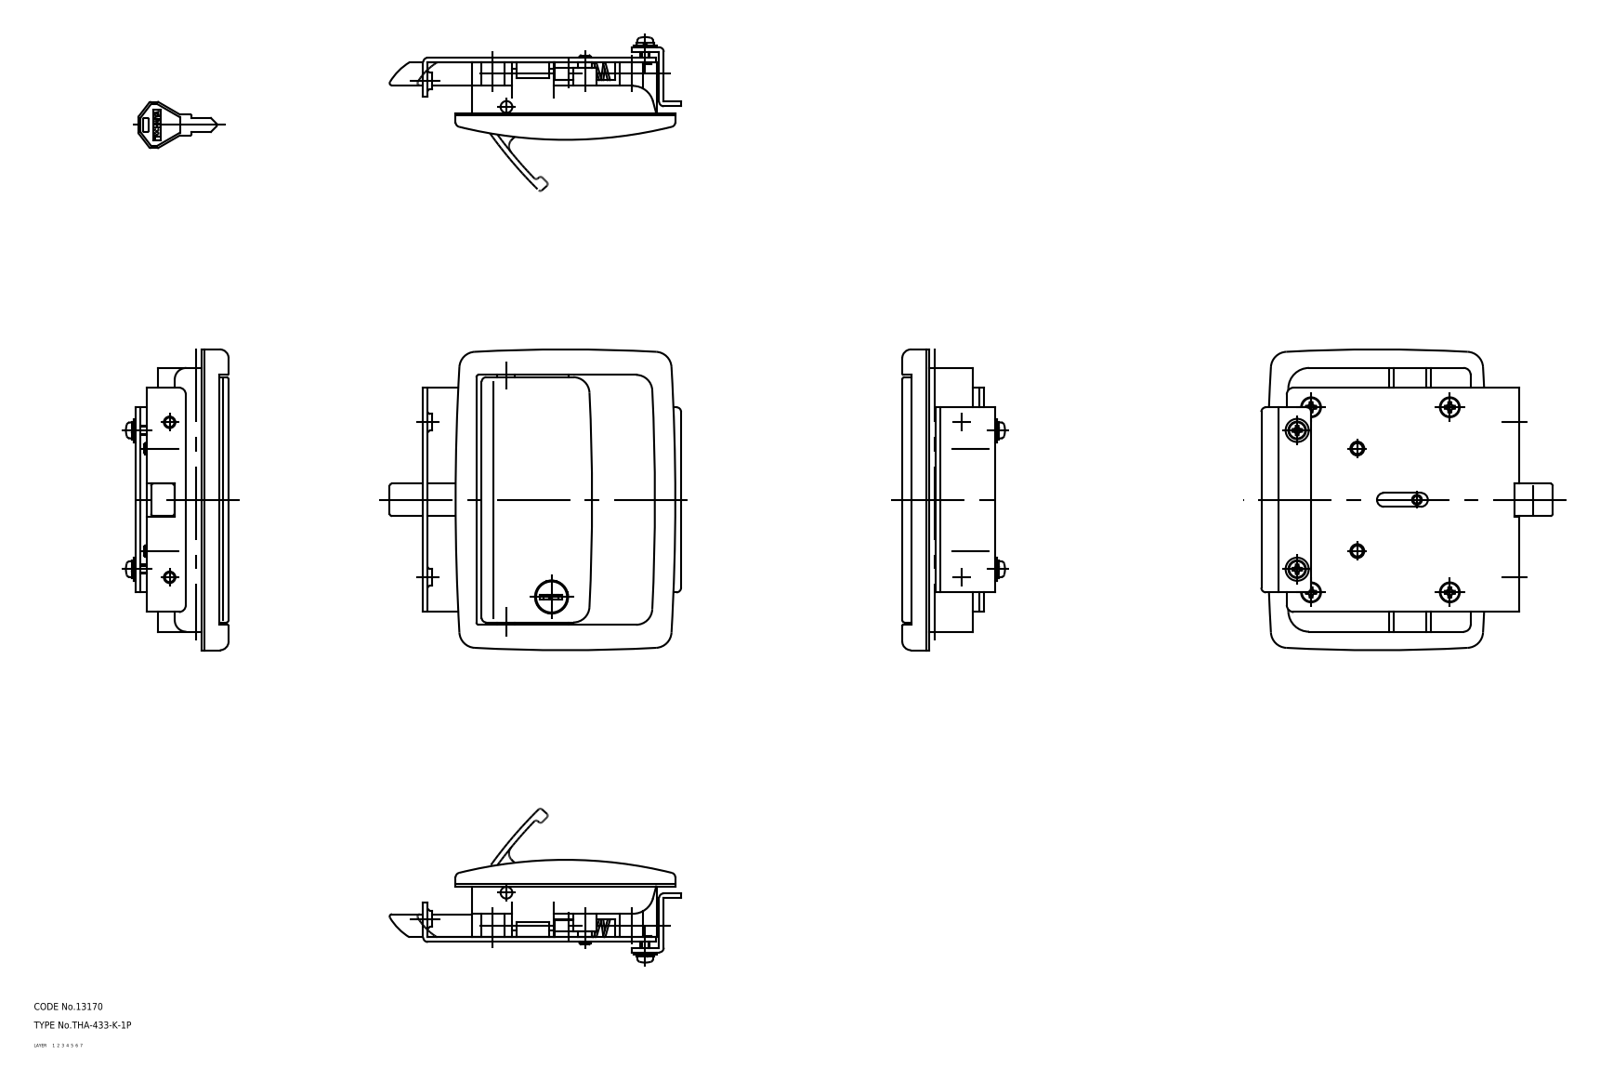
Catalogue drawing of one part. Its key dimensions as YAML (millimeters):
part_name: "screw; shaft; packing; lock (+7 more)"
step_written_by: "CADfix (AUTOMOTIVE_DESIGN)"
units: millimeters
bodies: {solids: 11, faces: 547, planar: 0, cylindrical: 0, other: 547}
overall_size: [130, 129.66, 109.46]
volume: 130062
surface_area: 102950
